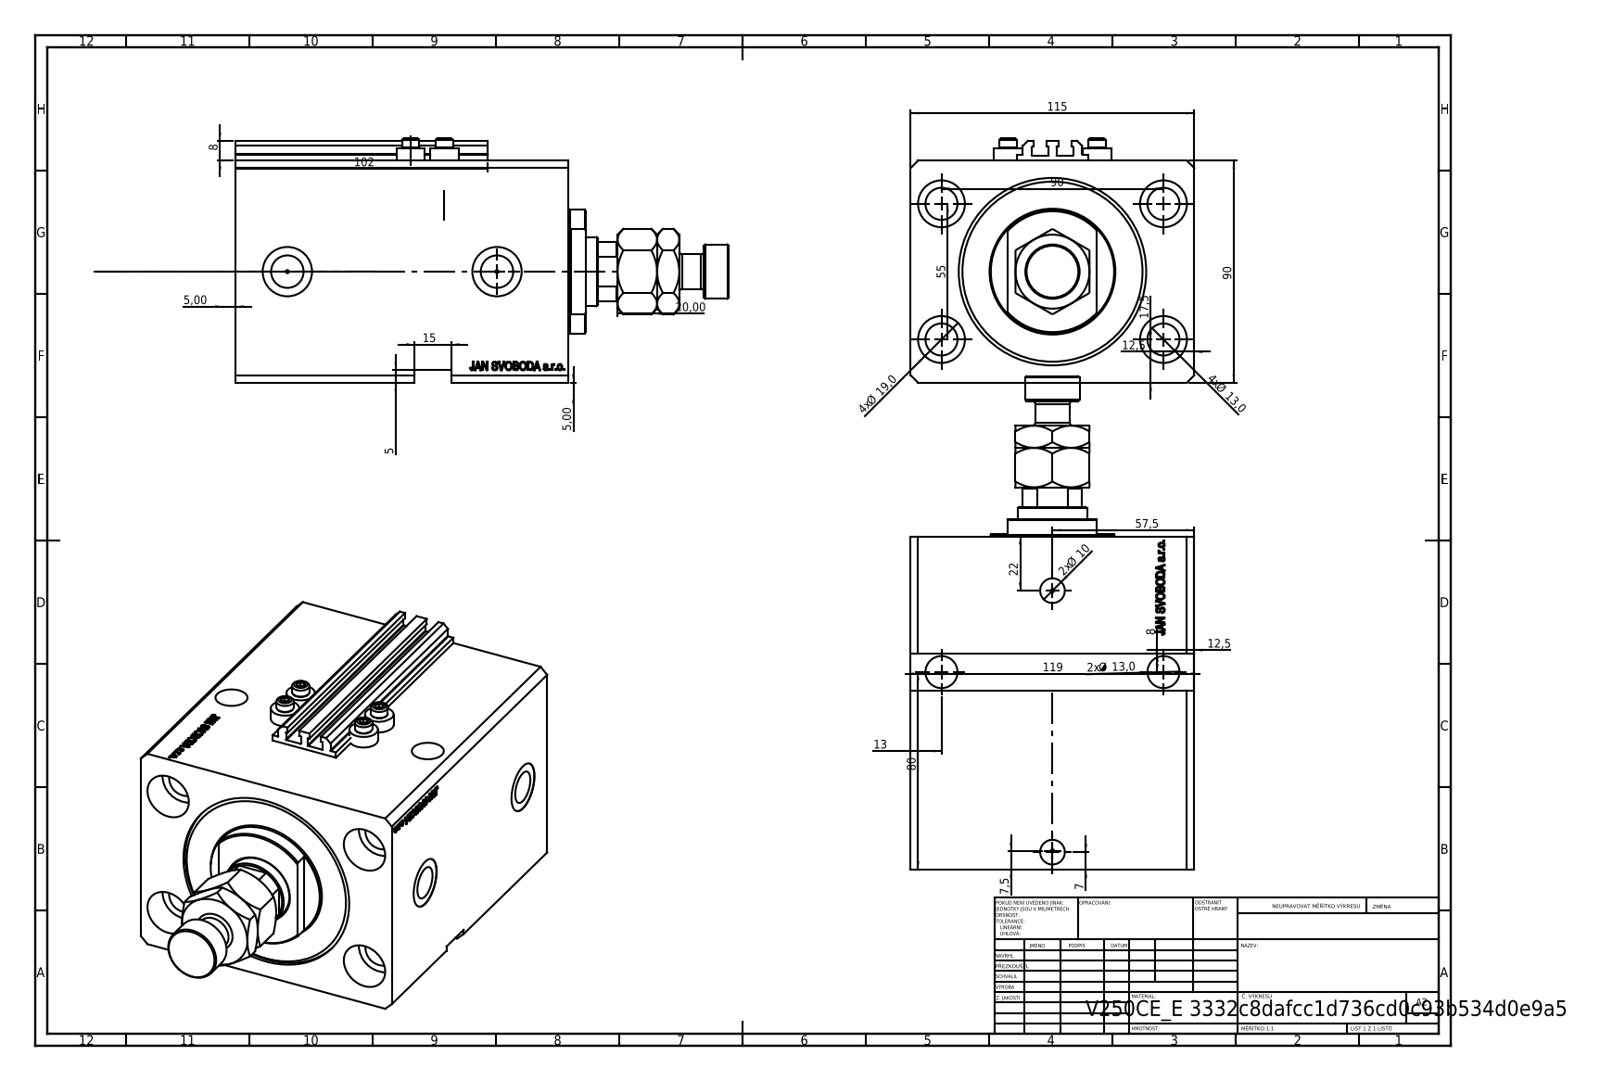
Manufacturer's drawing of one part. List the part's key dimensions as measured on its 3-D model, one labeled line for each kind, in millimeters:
Part name (STEP PRODUCT): V250CE_E_Body; V250CE_VC_E; V250CE_C_VCP; ALLEN BOLT V250CE (+1 more)
STEP written by: SolidWorks 2019 (CONFIG_CONTROL_DESIGN)
Units: millimetres
Bodies: 9 solids, 1175 faces (563 planar, 142 cylindrical, 470 other)
Overall size (bounding box): 199.9 × 115 × 99
Volume: 1 198 000 mm³ · Surface area: 191 830 mm²
Round holes (diameter × count): ⌀13 ×6, ⌀1.25 ×4, ⌀4 ×4, ⌀19 ×4, ⌀10 ×2, ⌀13.16 ×2, ⌀20 ×2, ⌀18.5 ×1, ⌀28 ×1, ⌀63 ×1, ⌀76 ×1
Round bosses / shafts (diameter × count): ⌀11.6 ×4, ⌀7 ×4, ⌀50 ×1, ⌀22 ×1, ⌀14 ×1
Partial cylindrical surfaces — rounded edges, fillets, slot ends (radius × count): R0.2 ×10, R13.5 ×1
Main face-to-face distances: 90, 115, 135, 87, 17.9, 117.1, 104.9, 30.1, 50, 54.9
Hole centre spacings: 52.74, 90, 13.6, 27.39, 28.46, 33.62, 36, 38.48
